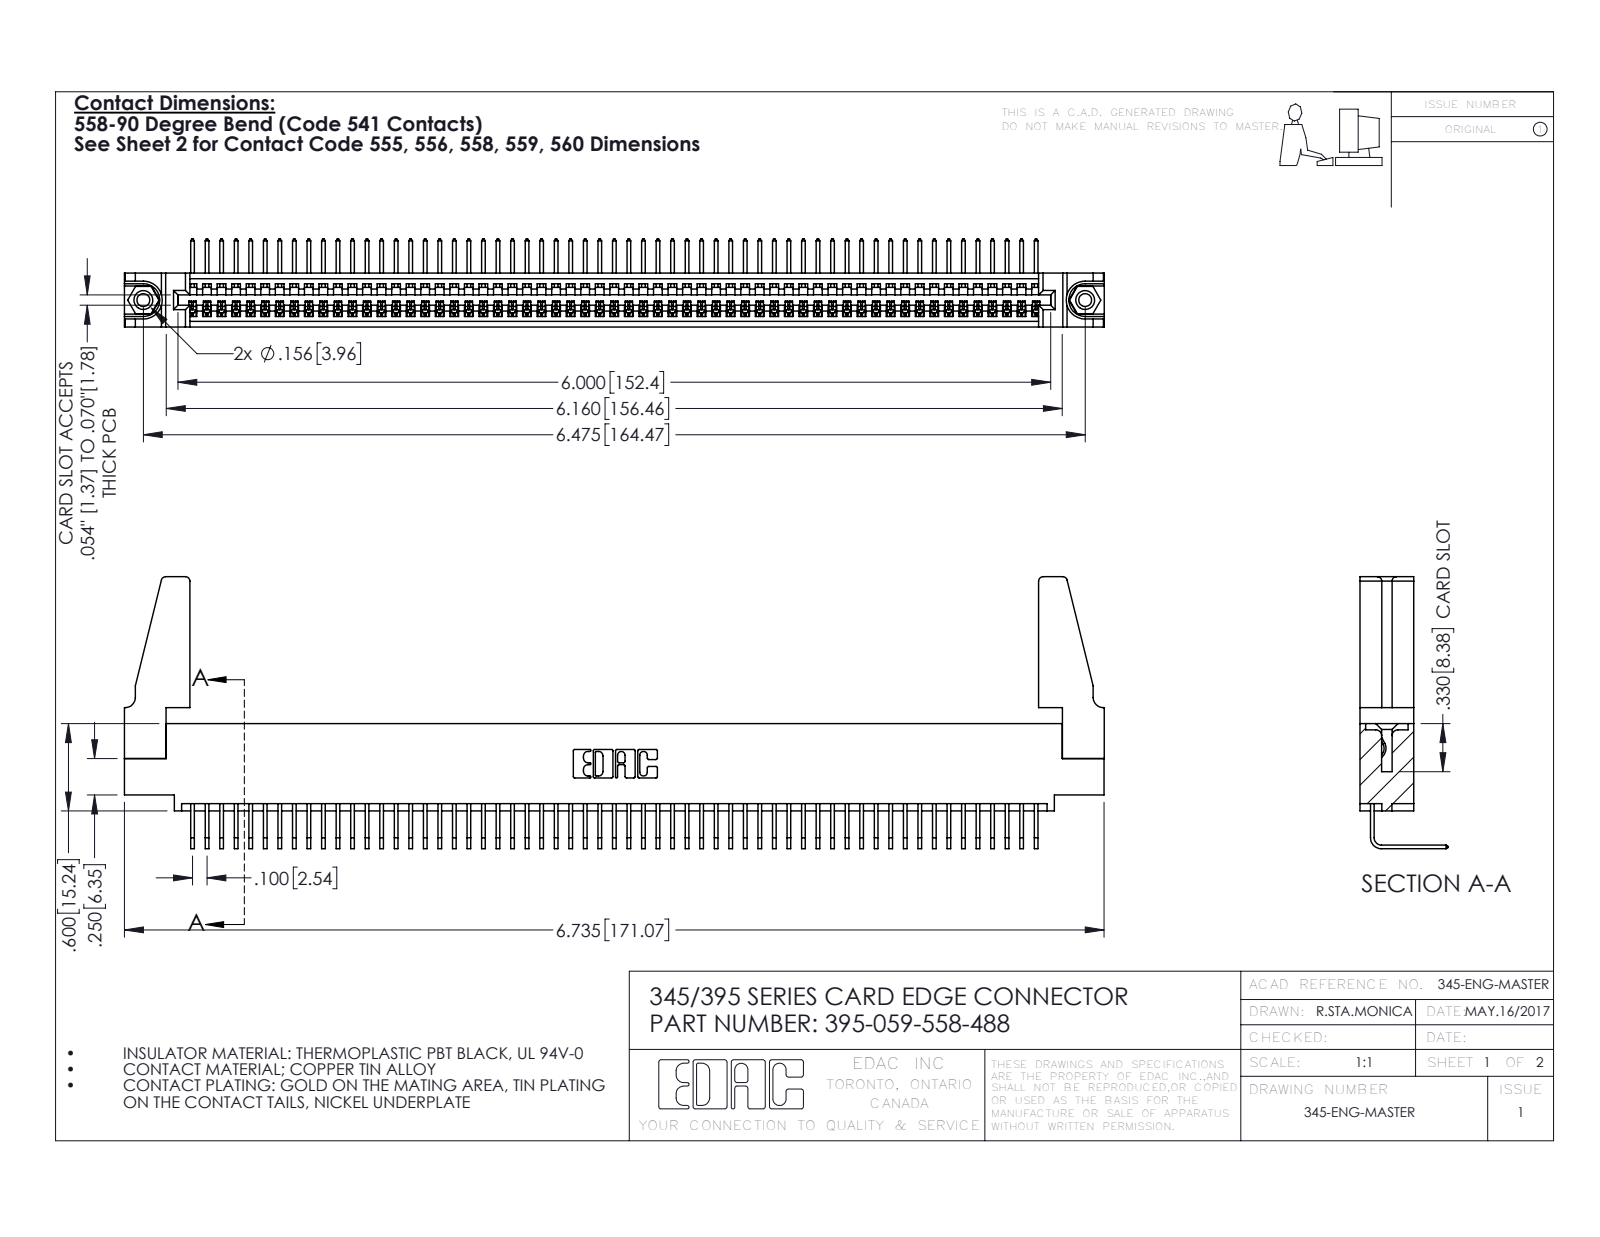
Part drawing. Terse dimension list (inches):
name: 345-250-001_345-250-001-102; 345-220-078_345-220-088; 345 Part_0.110 Offset - 0.156 Dia-TH; 345-292-001_558 Tail - 2 (+1 more)
written by: SolidWorks 2016 (CONFIG_CONTROL_DESIGN)
unit: in
bodies: 64 solids, 3794 faces (2634 planar, 1144 cylindrical, 16 other)
size: 6.736 × 1.869 × 0.605
volume: 1.206 in³; area: 41.14 in²
holes: 2× ⌀0.089, 2× ⌀0.125, 2× ⌀0.156, 1× ⌀0.064
bosses: 2× ⌀0.155
rounds: 118× R0.006, 22× R0.01, 8× R0.03, 6× R0.007, 6× R0.031, 3× R0.026, 2× R0.031, 2× R0.04
face distances: 0.072, 0.298, 0.37, 0.2, 0.098, 0.272, 0.025, 0.225, 0.149, 0.072
hole spacings: 0.27, 6.239, 6.475
